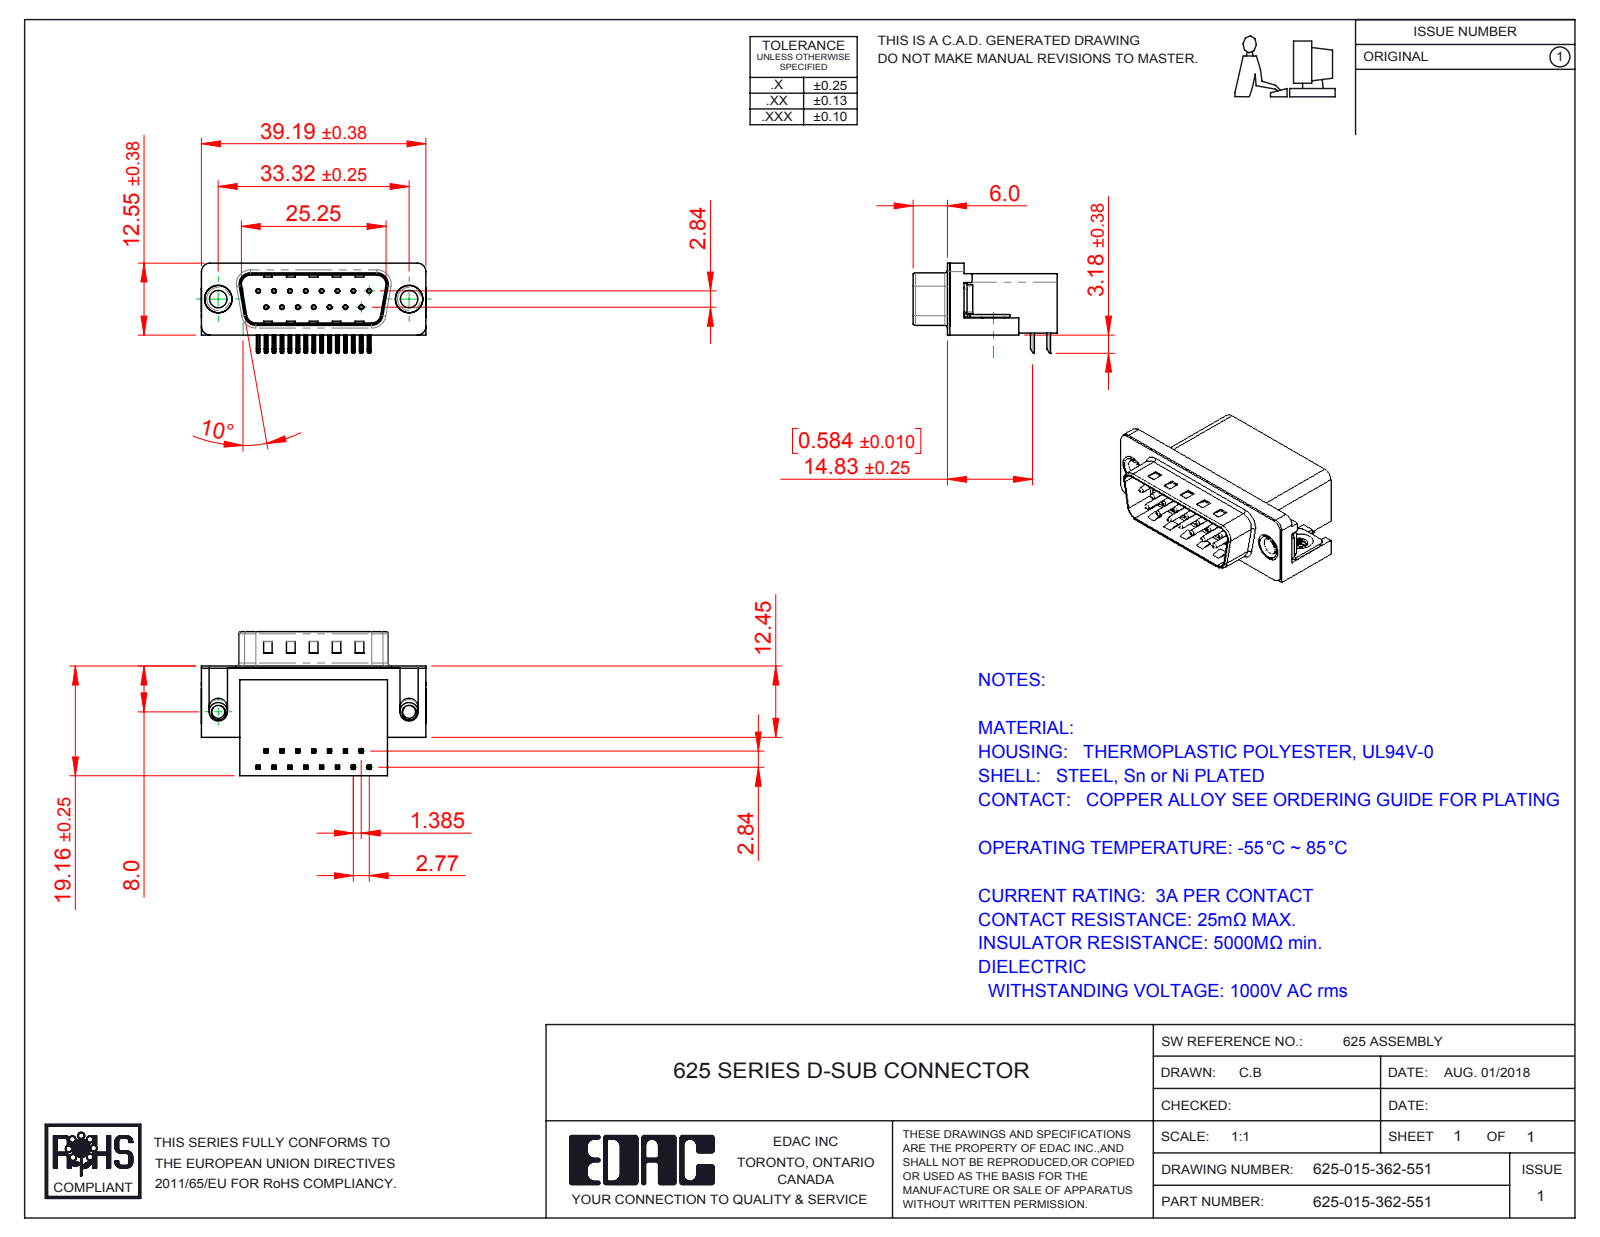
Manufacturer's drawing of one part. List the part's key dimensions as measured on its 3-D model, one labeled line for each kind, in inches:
Part name (STEP PRODUCT): 625-015-362-551; 625 Shell_15 Socket; 625 Thru Hole Rivet; 625 4-40 Threaded Board Mount (+3 more)
STEP written by: SolidWorks 2016 (CONFIG_CONTROL_DESIGN)
Units: inches
Bodies: 21 solids, 1471 faces (895 planar, 441 cylindrical, 135 other)
Overall size (bounding box): 1.544 × 0.991 × 0.619
Volume: 0.381 in³ · Surface area: 10.04 in²
Round holes (diameter × count): ⌀0.014 ×15, ⌀0.031 ×15, ⌀0.089 ×2, ⌀0.12 ×2, ⌀0.157 ×2, ⌀0.189 ×2, ⌀0.197 ×2
Round bosses / shafts (diameter × count): ⌀0.03 ×15, ⌀0.193 ×2, ⌀0.187 ×2, ⌀0.152 ×2, ⌀0.128 ×2
Partial cylindrical surfaces — rounded edges, fillets, slot ends (radius × count): R0.01 ×68, R0.005 ×30, R0.039 ×16, R0.02 ×9, R0.063 ×8, R0.059 ×6, R0.035 ×4, R0.079 ×4
Main face-to-face distances: 0.016, 0.407, 0.739, 0.083, 0.754, 0.412, 0.067, 0.428, 0.345, 0.64
Hole centre spacings: 0.124, 0.109, 0.218, 0.327, 0.436, 0.198, 0.198, 0.294
